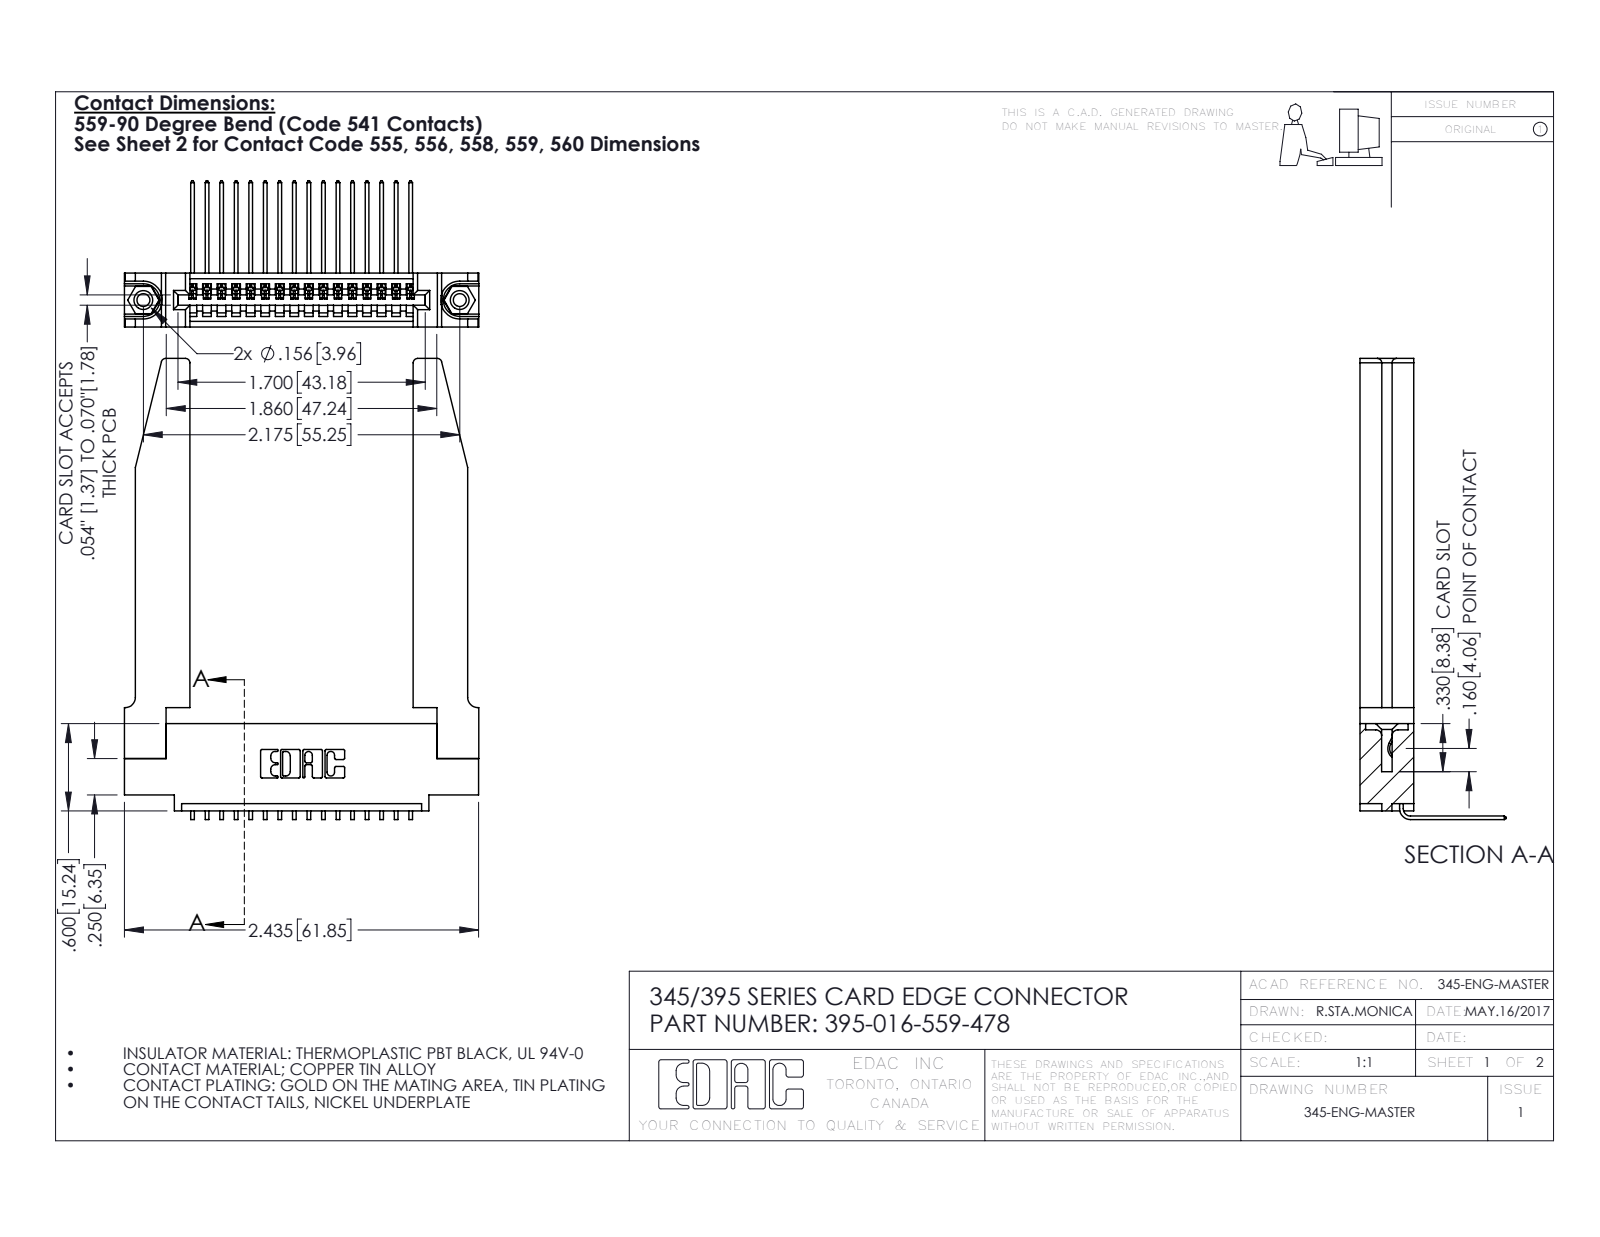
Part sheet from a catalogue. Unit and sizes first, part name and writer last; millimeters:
Units: millimetres
Overall size (bounding box): 80.5 × 61.9 × 25.5
Round holes (diameter × count): ⌀2.3 ×2, ⌀3.2 ×2, ⌀4 ×2, ⌀1.6 ×1
Round bosses / shafts (diameter × count): ⌀3.9 ×2
Partial cylindrical surfaces — rounded edges, fillets, slot ends (radius × count): R0.2 ×32, R0.3 ×22, R0.8 ×8, R0.2 ×6, R0.8 ×6, R0.7 ×3, R0.8 ×2, R1 ×2
Main face-to-face distances: 9.4, 1.8, 7.6, 3.8, 3.8, 5.1, 5.6, 2, 39, 2.5
Hole centre spacings: 6.9, 49.3, 55.2
Volume: 13 400 mm³ · Surface area: 14 390 mm²
Bodies: 21 solids, 1324 faces (898 planar, 374 cylindrical, 52 other)
Part name (STEP PRODUCT): 345-250-001_345-250-001-102; 395-016-559-478; 345 Part_0.110 Offset - 0.156 Dia-TH; 345-220-078_345-220-078 (+1 more)
STEP written by: SolidWorks 2016 (CONFIG_CONTROL_DESIGN)
